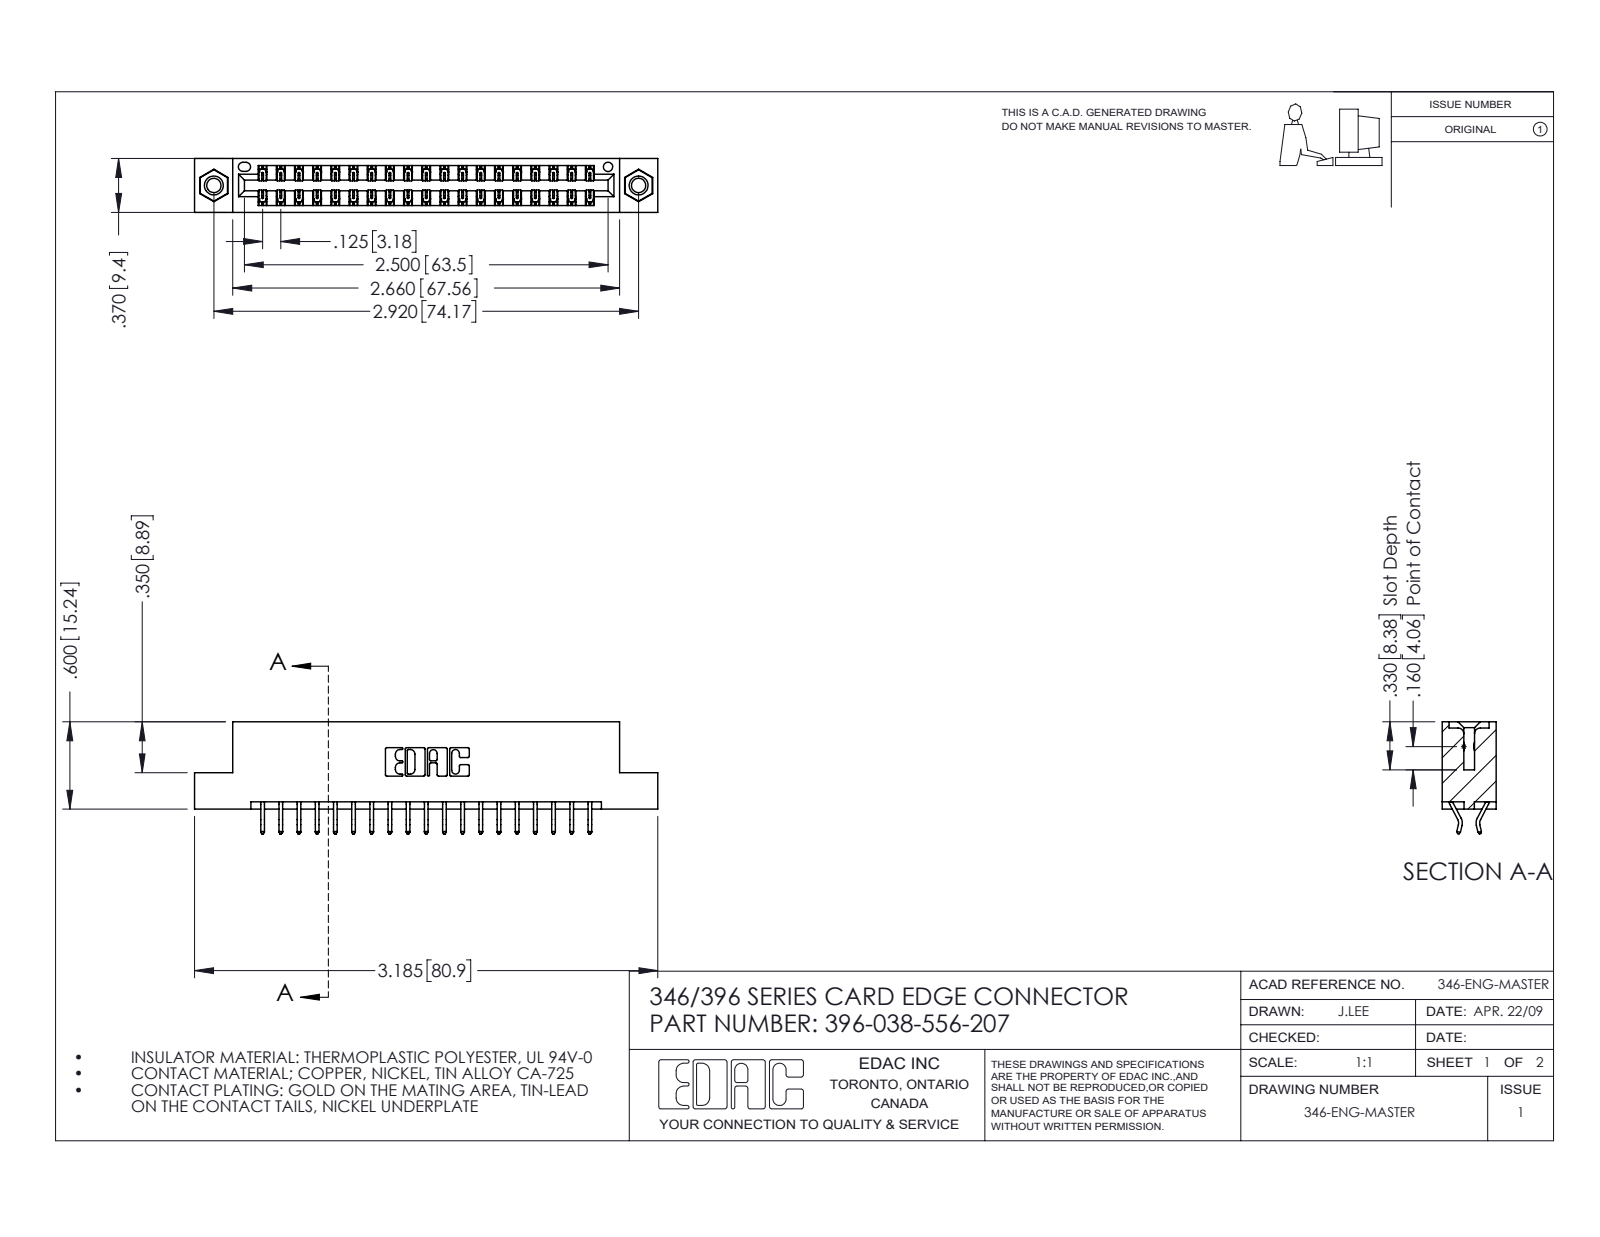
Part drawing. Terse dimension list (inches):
name: 346 Part_Flush Mounting Lugs - 0.156 Dia-TI; 345-292-001_556 Tail; 396-038-556-207; 345-250-001_345-250-005-103
written by: SolidWorks 2016 (CONFIG_CONTROL_DESIGN)
unit: in
bodies: 41 solids, 2386 faces (1590 planar, 780 cylindrical, 16 other)
size: 3.185 × 0.77 × 0.37
volume: 0.47 in³; area: 15.83 in²
holes: 2× ⌀0.098, 2× ⌀0.125, 2× ⌀0.156, 1× ⌀0.064
bosses: 2× ⌀0.155
rounds: 57× R0.006, 22× R0.01, 6× R0.007, 6× R0.031, 3× R0.026, 2× R0.01, 2× R0.014, 2× R0.022
face distances: 0.048, 0.322, 0.37, 0.25, 0.025, 0.072, 0.298, 0.275, 0.148, 0.222
hole spacings: 0.246, 2.713, 2.92
